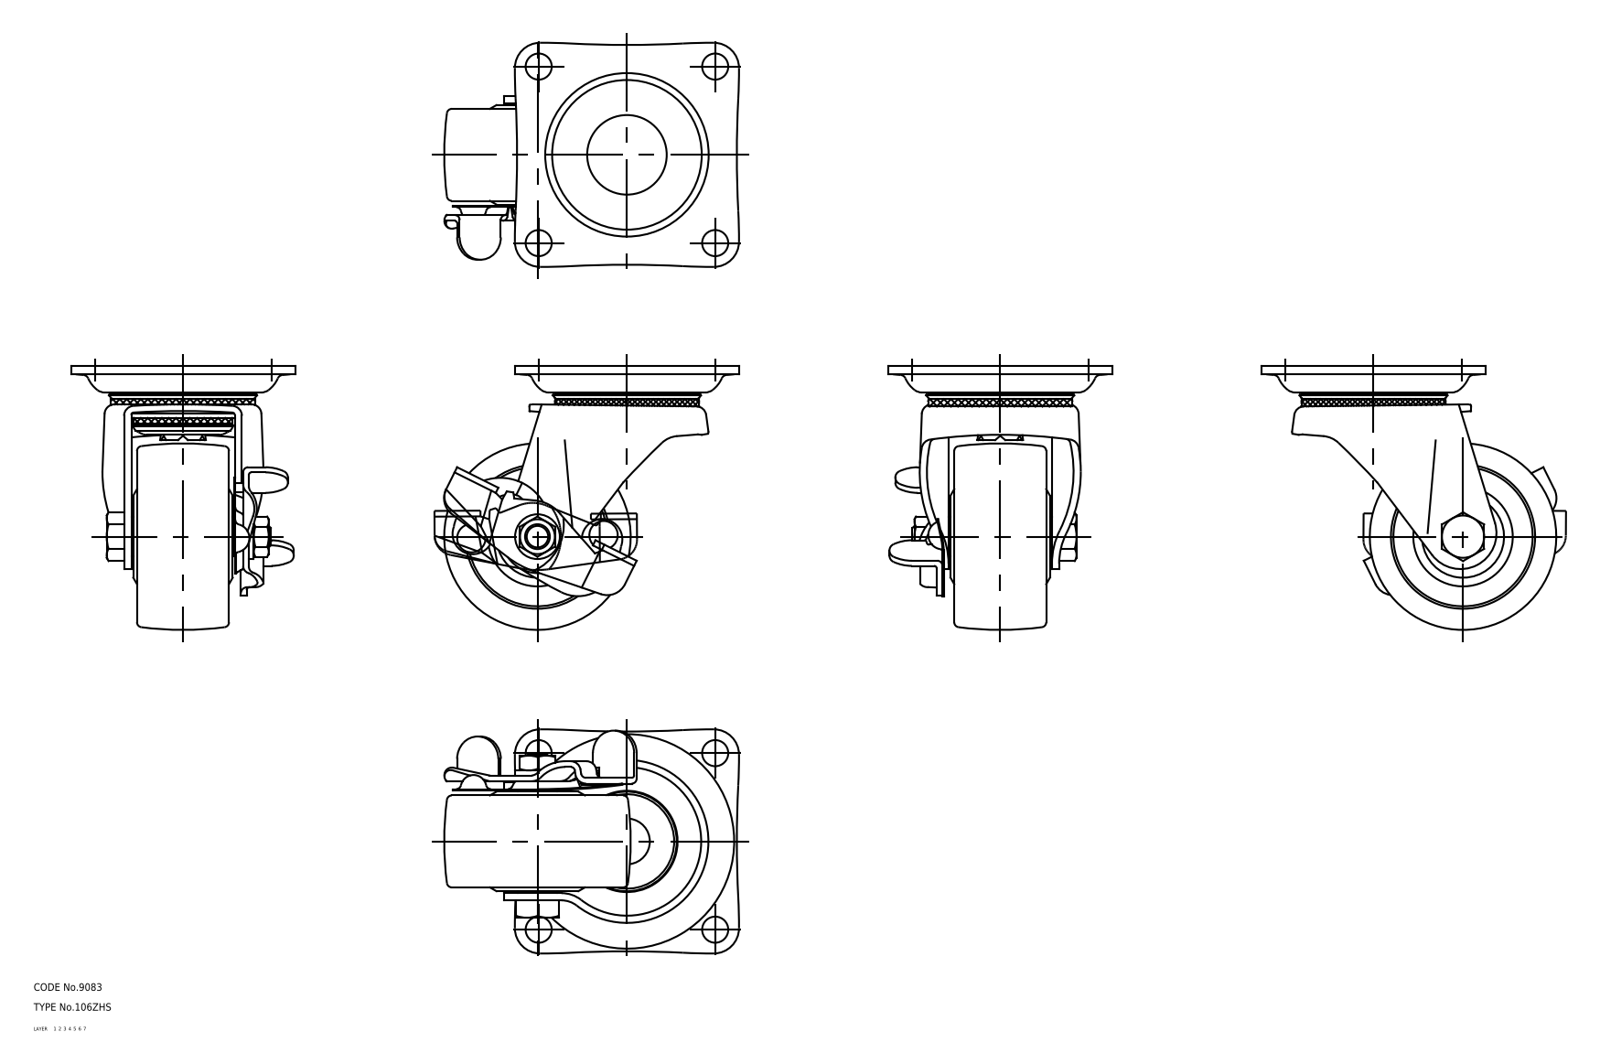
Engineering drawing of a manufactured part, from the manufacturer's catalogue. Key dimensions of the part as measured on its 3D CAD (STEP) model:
Part name (STEP PRODUCT): 67140503; 67140516; 67140529; 67140542 (+3 more)
STEP written by: CADfix (AUTOMOTIVE_DESIGN)
Units: millimetres
Bodies: 7 solids, 426 faces (0 planar, 0 cylindrical, 426 other)
Overall size (bounding box): 118.59 × 106 × 90.02
Volume: 264 468 mm³ · Surface area: 77 587 mm²
